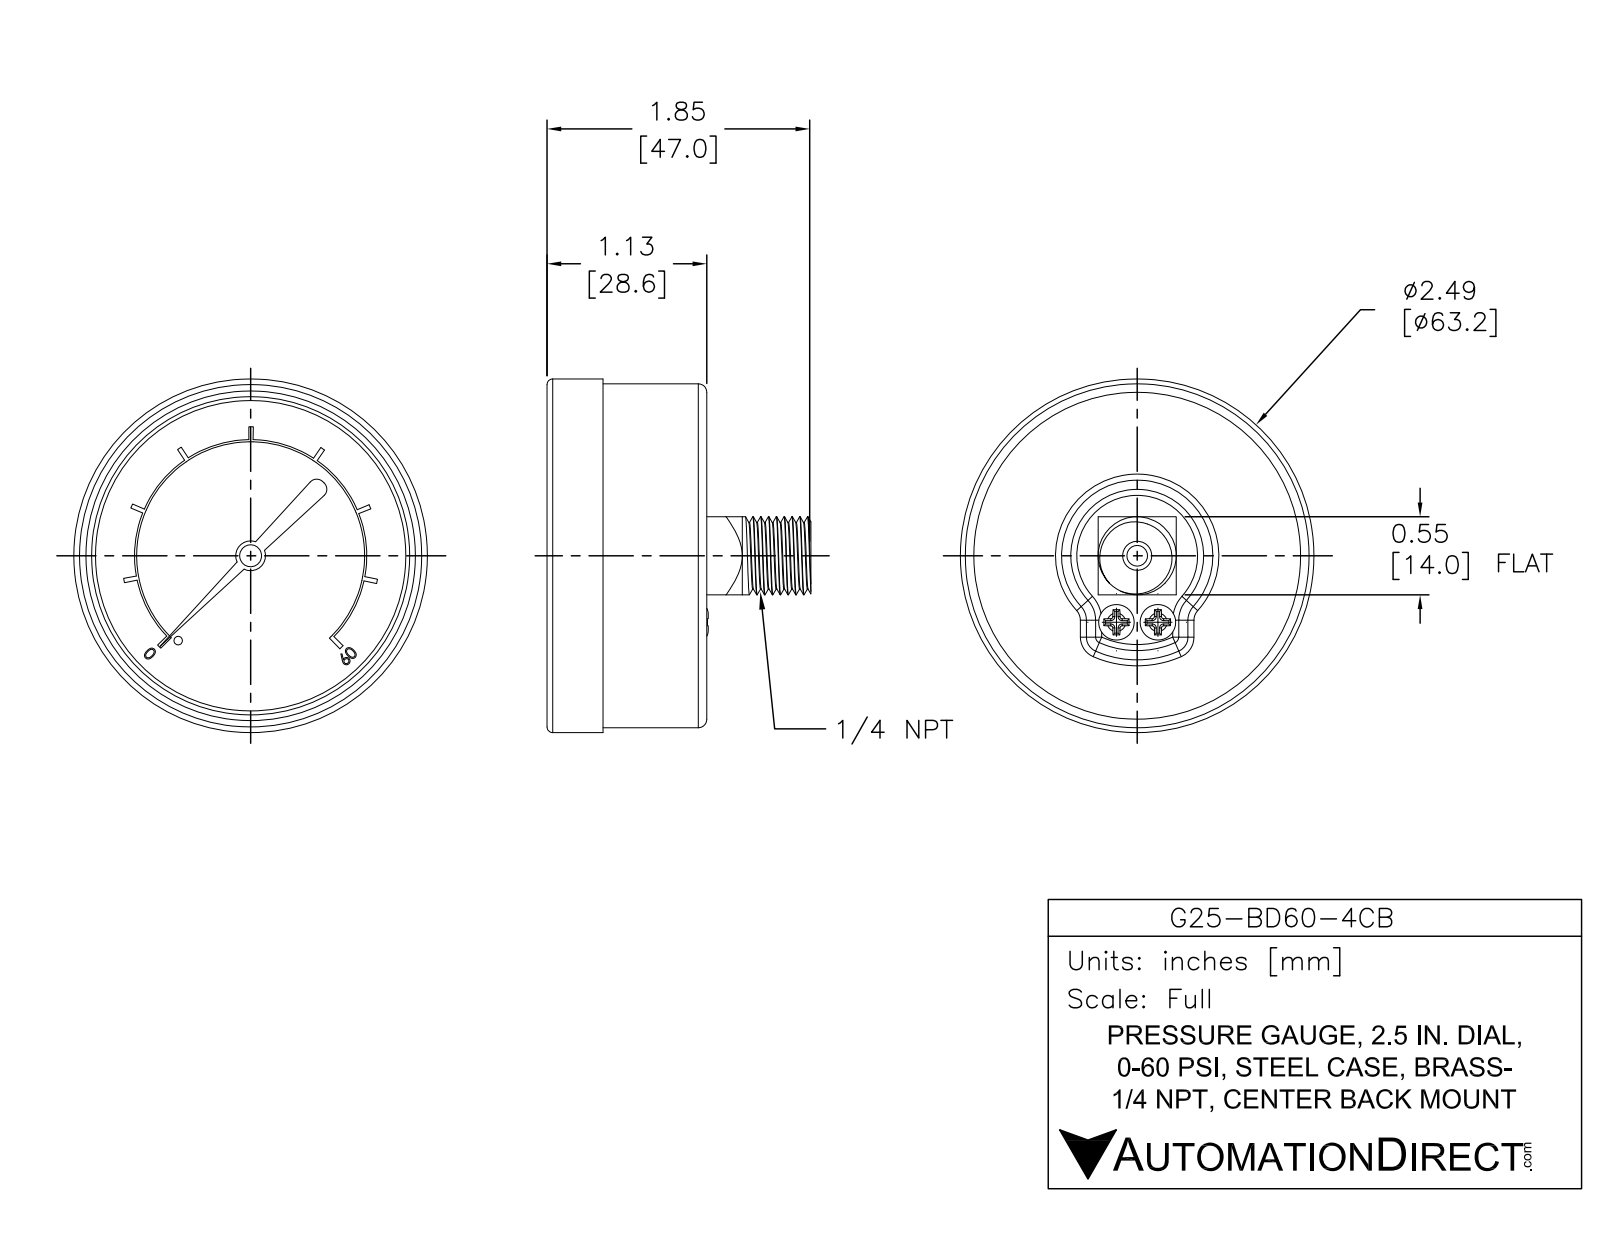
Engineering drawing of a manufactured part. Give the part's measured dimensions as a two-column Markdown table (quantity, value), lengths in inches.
| quantity | value |
| --- | --- |
| part name | G25-BD60-4CB |
| STEP written by | SolidWorks 2021 (AUTOMOTIVE_DESIGN) |
| units | inches |
| bodies | 1 solid, 195 faces (99 planar, 32 cylindrical, 64 other) |
| overall size | 2.49 × 2.49 × 1.858 |
| volume | 4.301 in³ |
| surface area | 22.47 in² |
| round holes (diameter × count) | 0.145 × 1, 2.185 × 1 |
| round bosses / shafts (diameter × count) | 0.25 × 2, 2.49 × 1, 2.421 × 1, 0.55 × 1, 0.178 × 1, 0.099 × 1, 0.04 × 1 |
| partial cylindrical surfaces (radius × count) | 0.06 × 4, 0.03 × 2, 0.115 × 1, 0.813 × 1, 0.823 × 1 |
| main face-to-face distances | 0.835, 0.1, 1.125, 0.29, 0.735, 1.025, 0.731, 0.631, 0.104, 0.394 |
